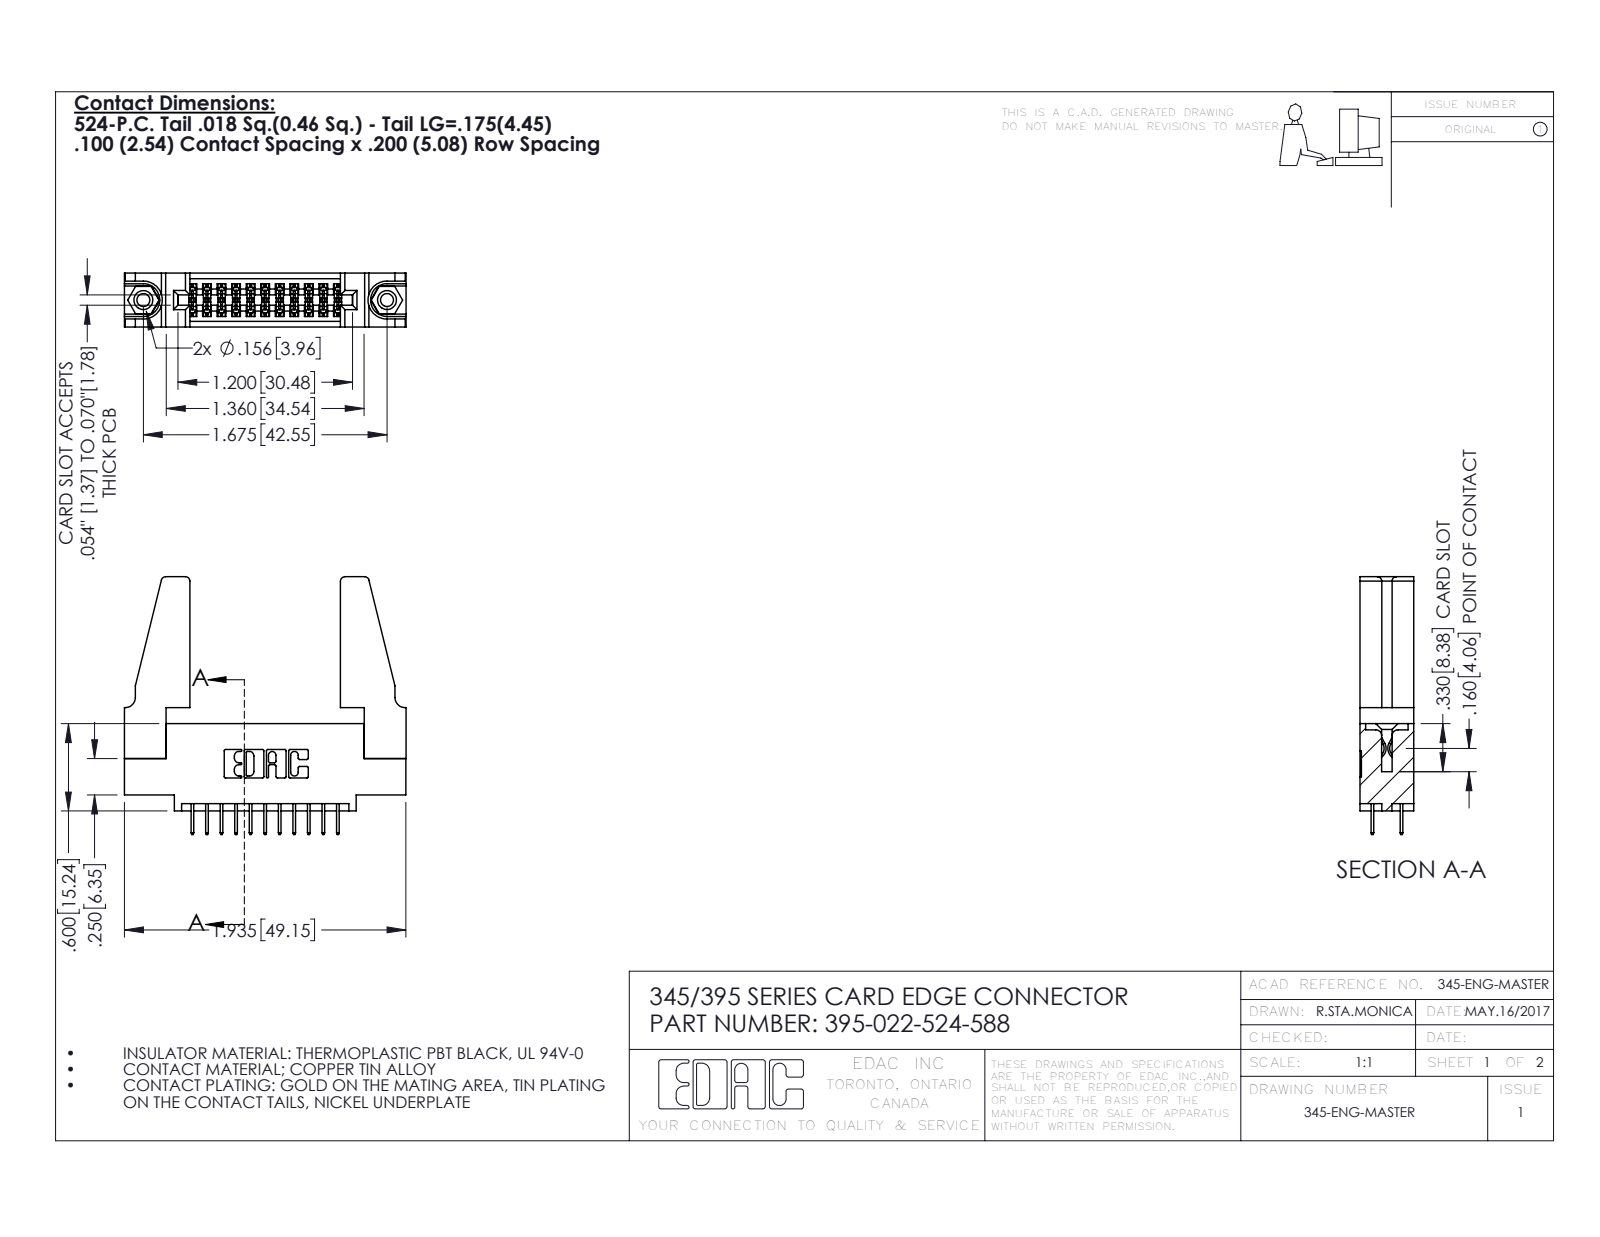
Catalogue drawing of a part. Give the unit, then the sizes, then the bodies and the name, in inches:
Units: inches
Overall size (bounding box): 1.936 × 1.772 × 0.37
Round holes (diameter × count): ⌀0.089 ×2, ⌀0.125 ×2, ⌀0.156 ×2, ⌀0.064 ×1
Round bosses / shafts (diameter × count): ⌀0.155 ×2
Partial cylindrical surfaces — rounded edges, fillets, slot ends (radius × count): R0.006 ×33, R0.01 ×22, R0.03 ×8, R0.007 ×6, R0.031 ×6, R0.026 ×3, R0.014 ×2, R0.019 ×2
Main face-to-face distances: 0.37, 0.072, 0.298, 0.2, 0.225, 0.098, 0.272, 0.025, 0.148, 0.15
Hole centre spacings: 0.27, 1.443, 1.675
Volume: 0.466 in³ · Surface area: 13.96 in²
Bodies: 27 solids, 1442 faces (1014 planar, 412 cylindrical, 16 other)
Part name (STEP PRODUCT): 345 Part_0.110 Offset - 0.156 Dia-TH; 345-292-001_345-293-124; 345-250-001_345-250-001-102; 345-220-078_345-220-088 (+1 more)
STEP written by: SolidWorks 2016 (CONFIG_CONTROL_DESIGN)
